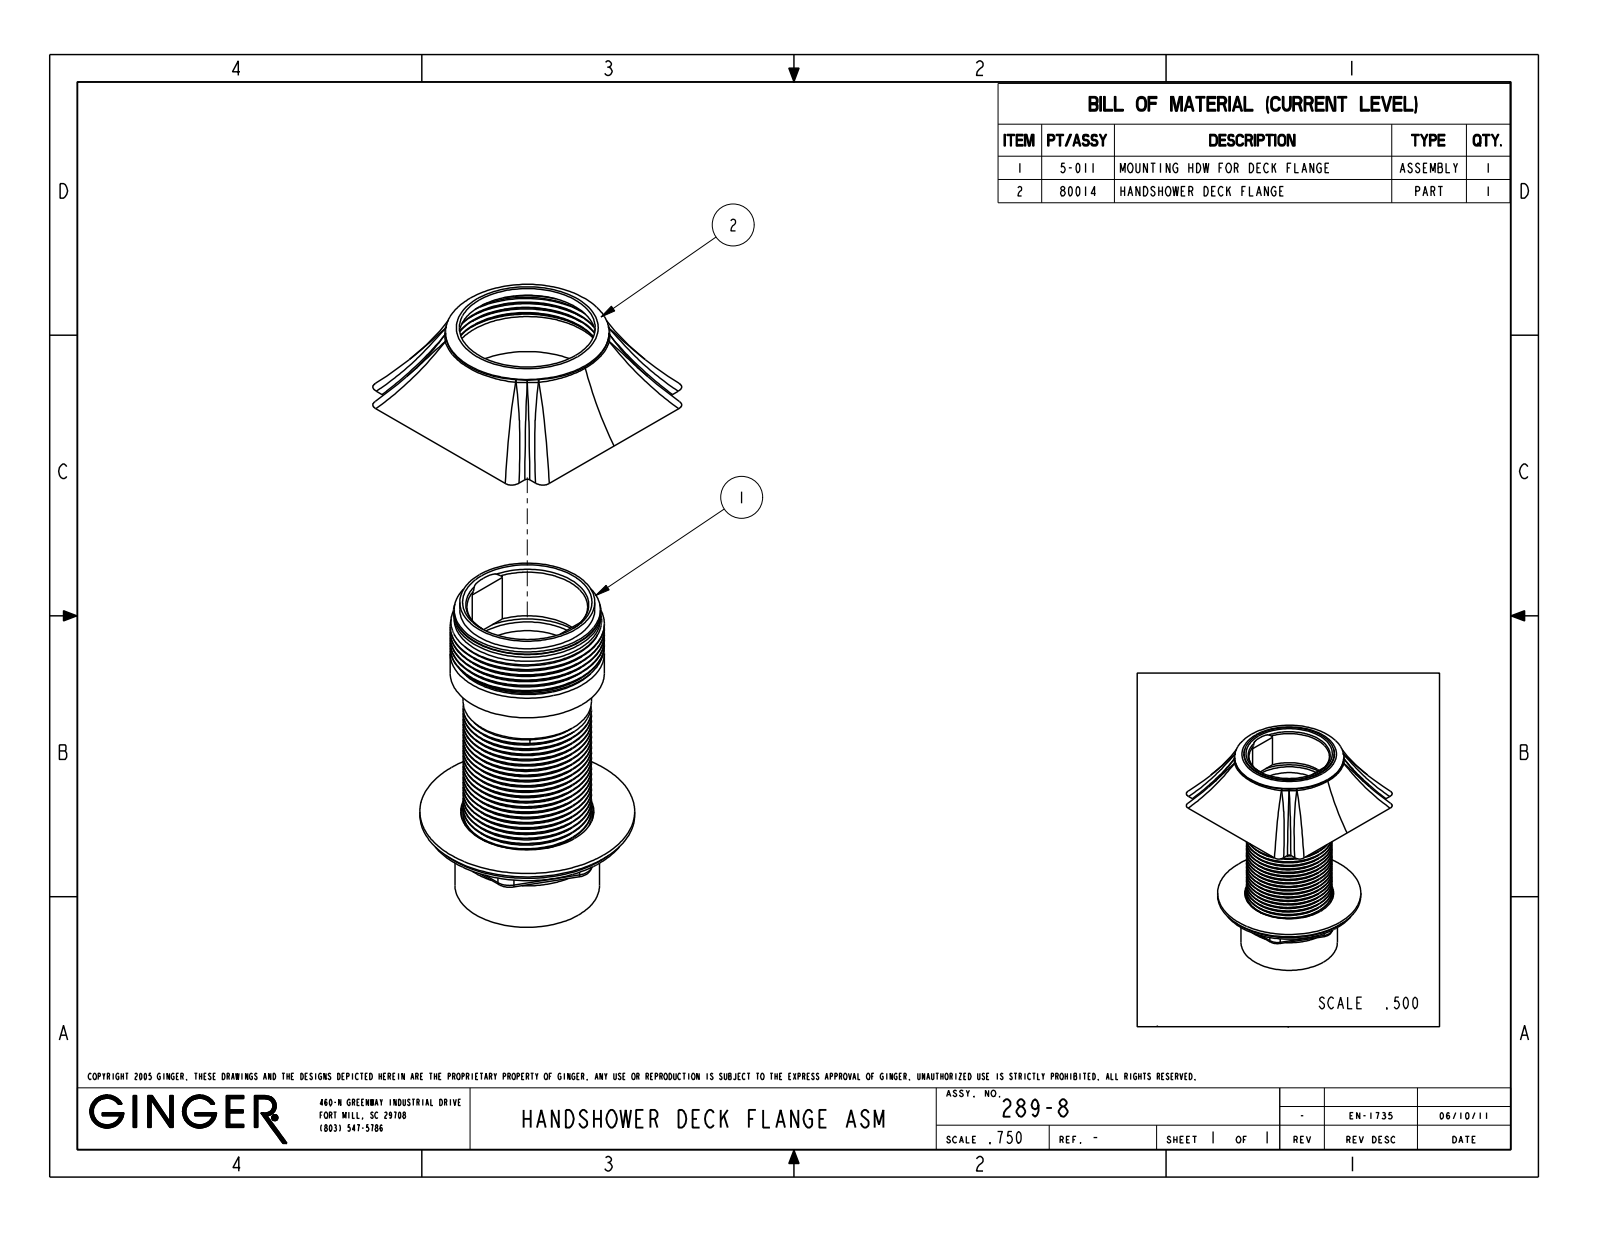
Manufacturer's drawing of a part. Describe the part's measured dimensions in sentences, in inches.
The part is named "289-8_SW0001". Its 3-D file was written by "PRO/ENGINEER BY PARAMETRIC TECHNOLOGY CORPORATION, 2009300 (CONFIG_CONTROL_DESIGN)". It is 0 solids with 312 faces: 28 planar, 145 cylindrical and 139 other. Overall it measures 3.18 by 2.25 by 2.25 inches. Round holes: 1 of diameter 1.01, 1 of diameter 1.025, 1 of diameter 1.15, 1 of diameter 1.22, 1 of diameter 1.235, 1 of diameter 1.373, 1 of diameter 1.437, 1 of diameter 1.438. Round bosses or shafts: 1 of diameter 2, 1 of diameter 1.969, 1 of diameter 1.895, 1 of diameter 1.5, 1 of diameter 1.413, 1 of diameter 1.352, 1 of diameter 1.349, 1 of diameter 1.34. Partial cylindrical surfaces (rounded edges, fillets, slot ends): 6 of radius 0.04, 6 of radius 0.15, 2 of radius 0.06, 1 of radius 0.553. The main face-to-face distances are 0.039, 1.612, 1.573, 1.602, 1.563, 0.092, 0.131, 1.694, 1.704, 1.681.
